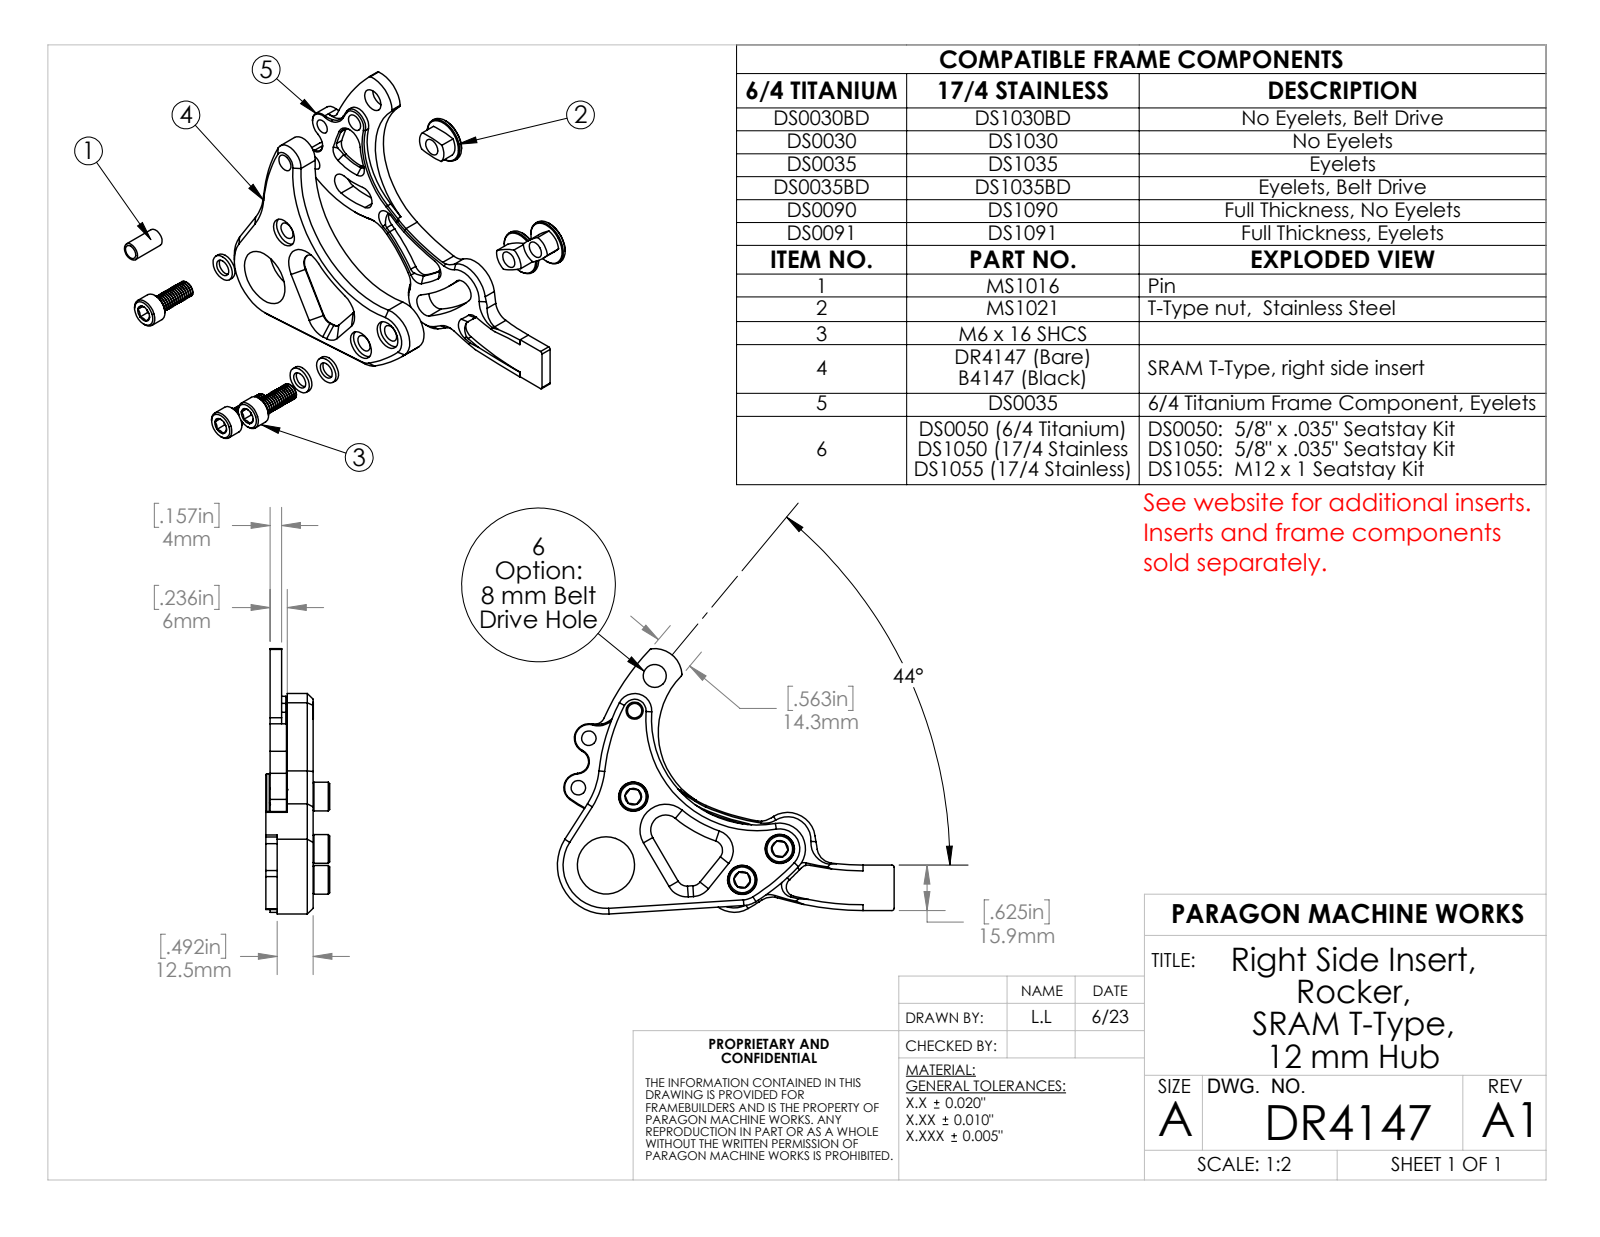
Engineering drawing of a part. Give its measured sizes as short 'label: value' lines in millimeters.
name: DR4147
written by: SolidWorks 2022 (AUTOMOTIVE_DESIGN)
unit: mm
bodies: 1 solid, 86 faces (23 planar, 46 cylindrical, 17 other)
size: 81.22 × 77.21 × 16.5
volume: 27 777 mm³; area: 10 662 mm²
holes: 3× ⌀6, 3× ⌀10.26, 1× ⌀5.99, 1× ⌀20
rounds: 6× R0.5, 3× R3.5, 2× R9, 1× R4, 1× R5.25, 1× R5.99, 1× R14.86, 1× R15
face distances: 9, 12.5, 3.5, 4, 5, 8.5, 7.5, 16.5, 1.5, 2.5
hole spacings: 70.01, 17.01, 25.84, 30, 47.83, 47.87, 54.33, 54.92
